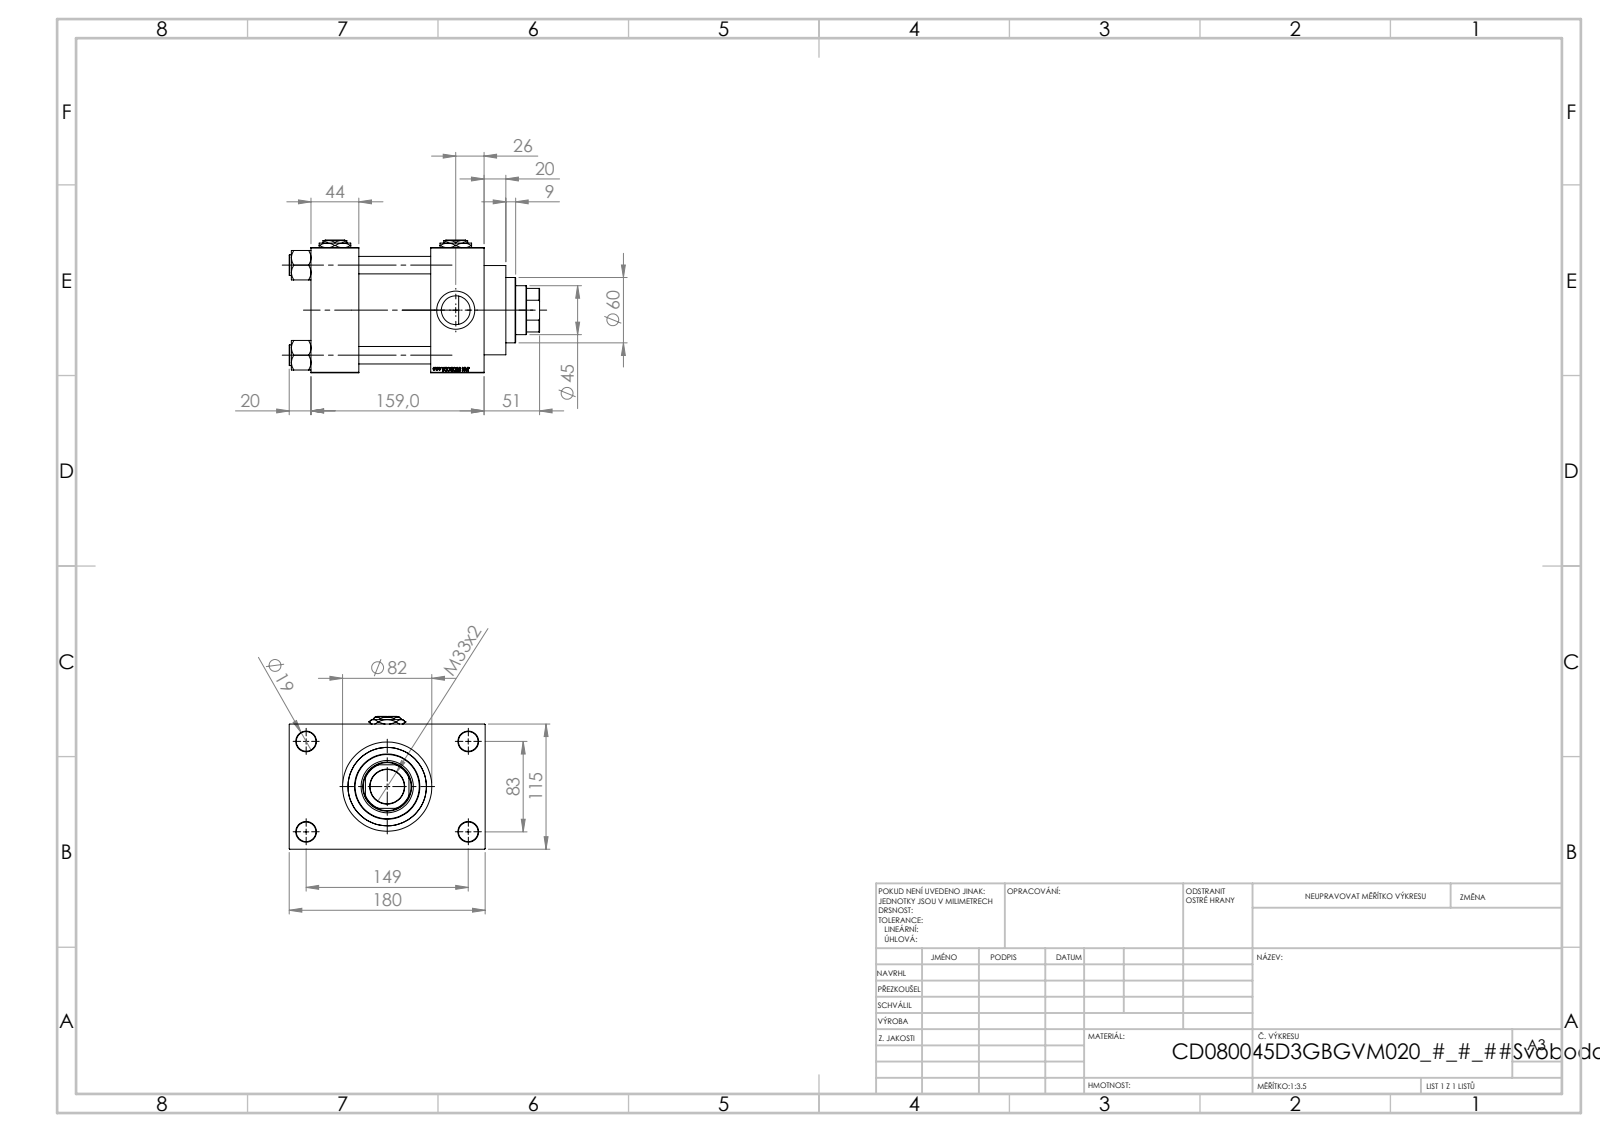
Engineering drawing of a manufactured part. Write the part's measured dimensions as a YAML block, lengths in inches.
part_name: "V215CD_VC_A; V215CD_D_TYCINKA; V215CD_NUT_M5_D; Zatka_pro_OIL_PORT (+2 more)"
step_written_by: "SolidWorks 2019 (CONFIG_CONTROL_DESIGN)"
units: inches
bodies: {solids: 13, faces: 1252, planar: 593, cylindrical: 99, other: 560}
overall_size: [9.055, 7.087, 4.803]
volume: 121.5
surface_area: 479
round_holes:
  - {diameter: 0.63, count: 4}
  - {diameter: 0.709, count: 4}
  - {diameter: 1.041, count: 4}
  - {diameter: 1.378, count: 4}
  - {diameter: 0.276, count: 3}
  - {diameter: 1.24, count: 1}
  - {diameter: 1.772, count: 1}
  - {diameter: 1.89, count: 1}
  - {diameter: 2.402, count: 1}
  - {diameter: 2.835, count: 1}
  - {diameter: 3.15, count: 1}
round_bosses_or_shafts:
  - {diameter: 0.748, count: 4}
  - {diameter: 3.386, count: 1}
  - {diameter: 3.228, count: 1}
  - {diameter: 2.362, count: 1}
partial_cylinders:
  - {radius: 0.866, count: 1}
face_to_face_distances: [4.528, 4.331, 2.598, 1.929, 1.732, 6.26, 5.807, 1.28, 0.787, 2.717]
hole_center_spacings: [1.305, 2.302, 3.256, 3.357, 3.513, 4.561, 5.607, 3.268]
